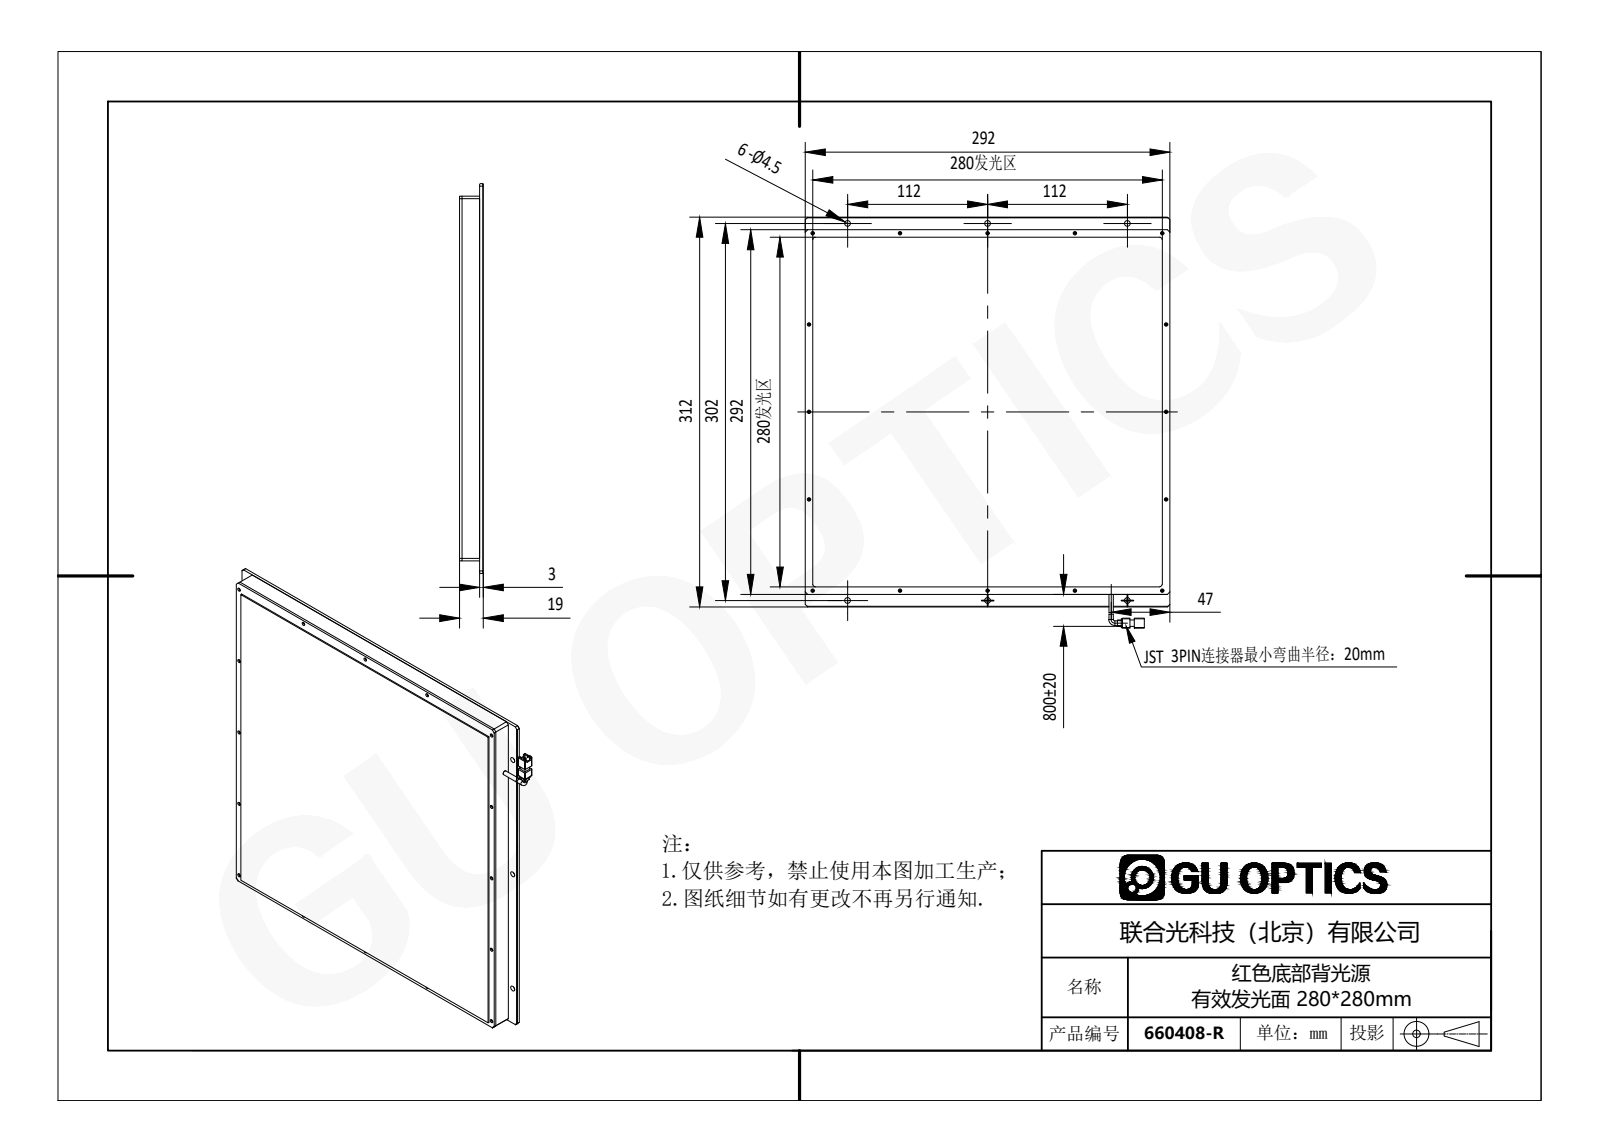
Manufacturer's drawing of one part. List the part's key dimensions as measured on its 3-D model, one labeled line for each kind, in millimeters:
Part name (STEP PRODUCT): 660408-R
STEP written by: SolidWorks 2016 (AUTOMOTIVE_DESIGN)
Units: millimetres
Bodies: 5 solids, 539 faces (169 planar, 270 cylindrical, 100 other)
Overall size (bounding box): 329 × 292 × 20
Volume: 614 608 mm³ · Surface area: 407 504 mm²
Round holes (diameter × count): ⌀1.6 ×32, ⌀1.25 ×16, ⌀1.5 ×16, ⌀2 ×16, ⌀2.4 ×16, ⌀2.8 ×16, ⌀4.5 ×6
Round bosses / shafts (diameter × count): ⌀3.5 ×2
Partial cylindrical surfaces — rounded edges, fillets, slot ends (radius × count): R0.5 ×8, R1 ×8, R2 ×6
Main face-to-face distances: 17, 3, 14, 20, 6, 286, 292, 16, 1, 280
Hole centre spacings: 286, 70, 294.44, 80, 210, 296.98, 140, 160.56
